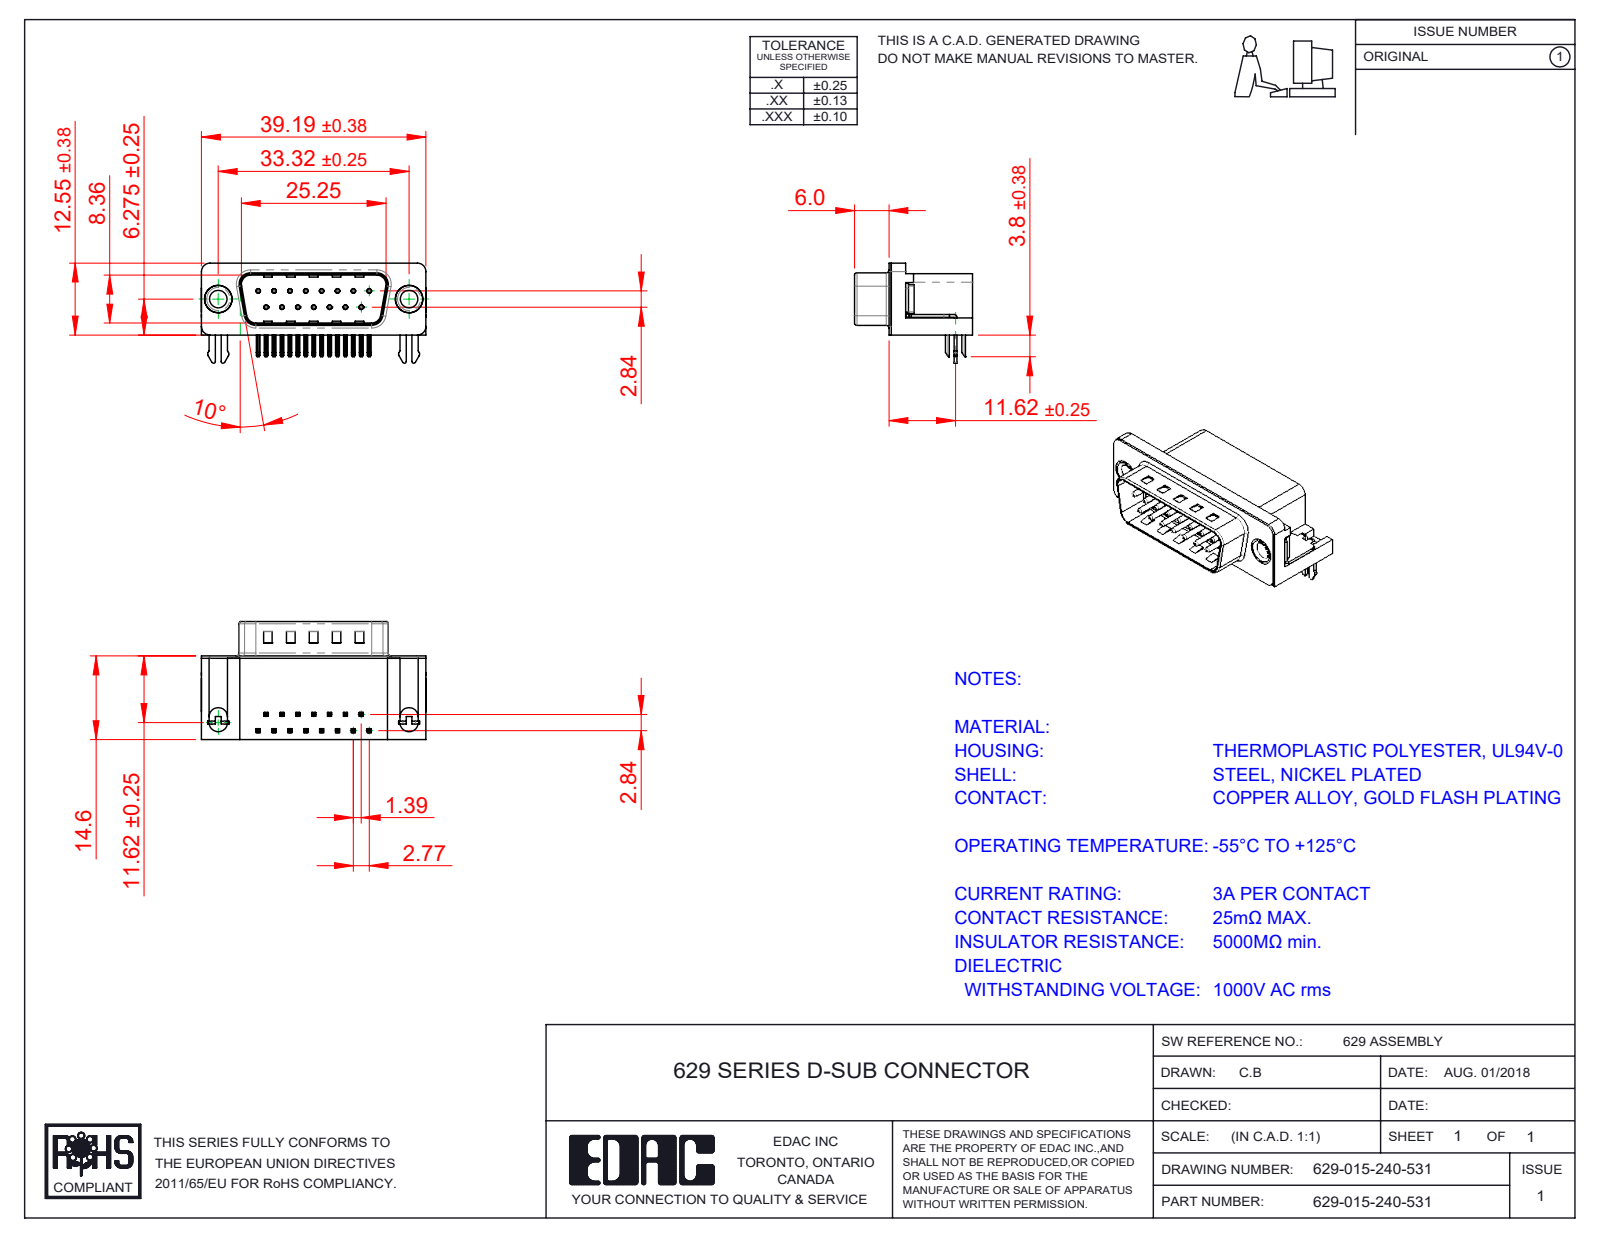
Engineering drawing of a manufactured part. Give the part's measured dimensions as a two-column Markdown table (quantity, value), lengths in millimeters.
| quantity | value |
| --- | --- |
| part name | 629 Contact Bottom; 629 2 Prong Board Lock; 629 Thru Hole Rivet; 629-015-240-531 (+3 more) |
| STEP written by | SolidWorks 2020 (CONFIG_CONTROL_DESIGN) |
| units | millimeters |
| bodies | 21 solids, 1475 faces (923 planar, 435 cylindrical, 117 other) |
| overall size | 39.22 × 20.6 × 17.48 |
| volume | 5 068 mm³ |
| surface area | 6 055 mm² |
| round holes (diameter × count) | 0.35 × 15, 0.8 × 15, 3.05 × 2, 4 × 2, 4.8 × 2, 5 × 2 |
| round bosses / shafts (diameter × count) | 0.75 × 15, 4.9 × 2, 4.75 × 2, 3.85 × 2 |
| partial cylindrical surfaces (radius × count) | 0.25 × 68, 0.12 × 30, 1 × 16, 0.5 × 14, 1.6 × 8, 1.5 × 6, 0.32 × 4, 0.9 × 4 |
| main face-to-face distances | 0.4, 14.2, 10.35, 2.1, 14.6, 10.46, 1.7, 10.86, 8.76, 0.5 |
| hole center spacings | 3.16, 2.77, 5.54, 8.31, 11.08, 5.03, 5.04, 7.48 |
